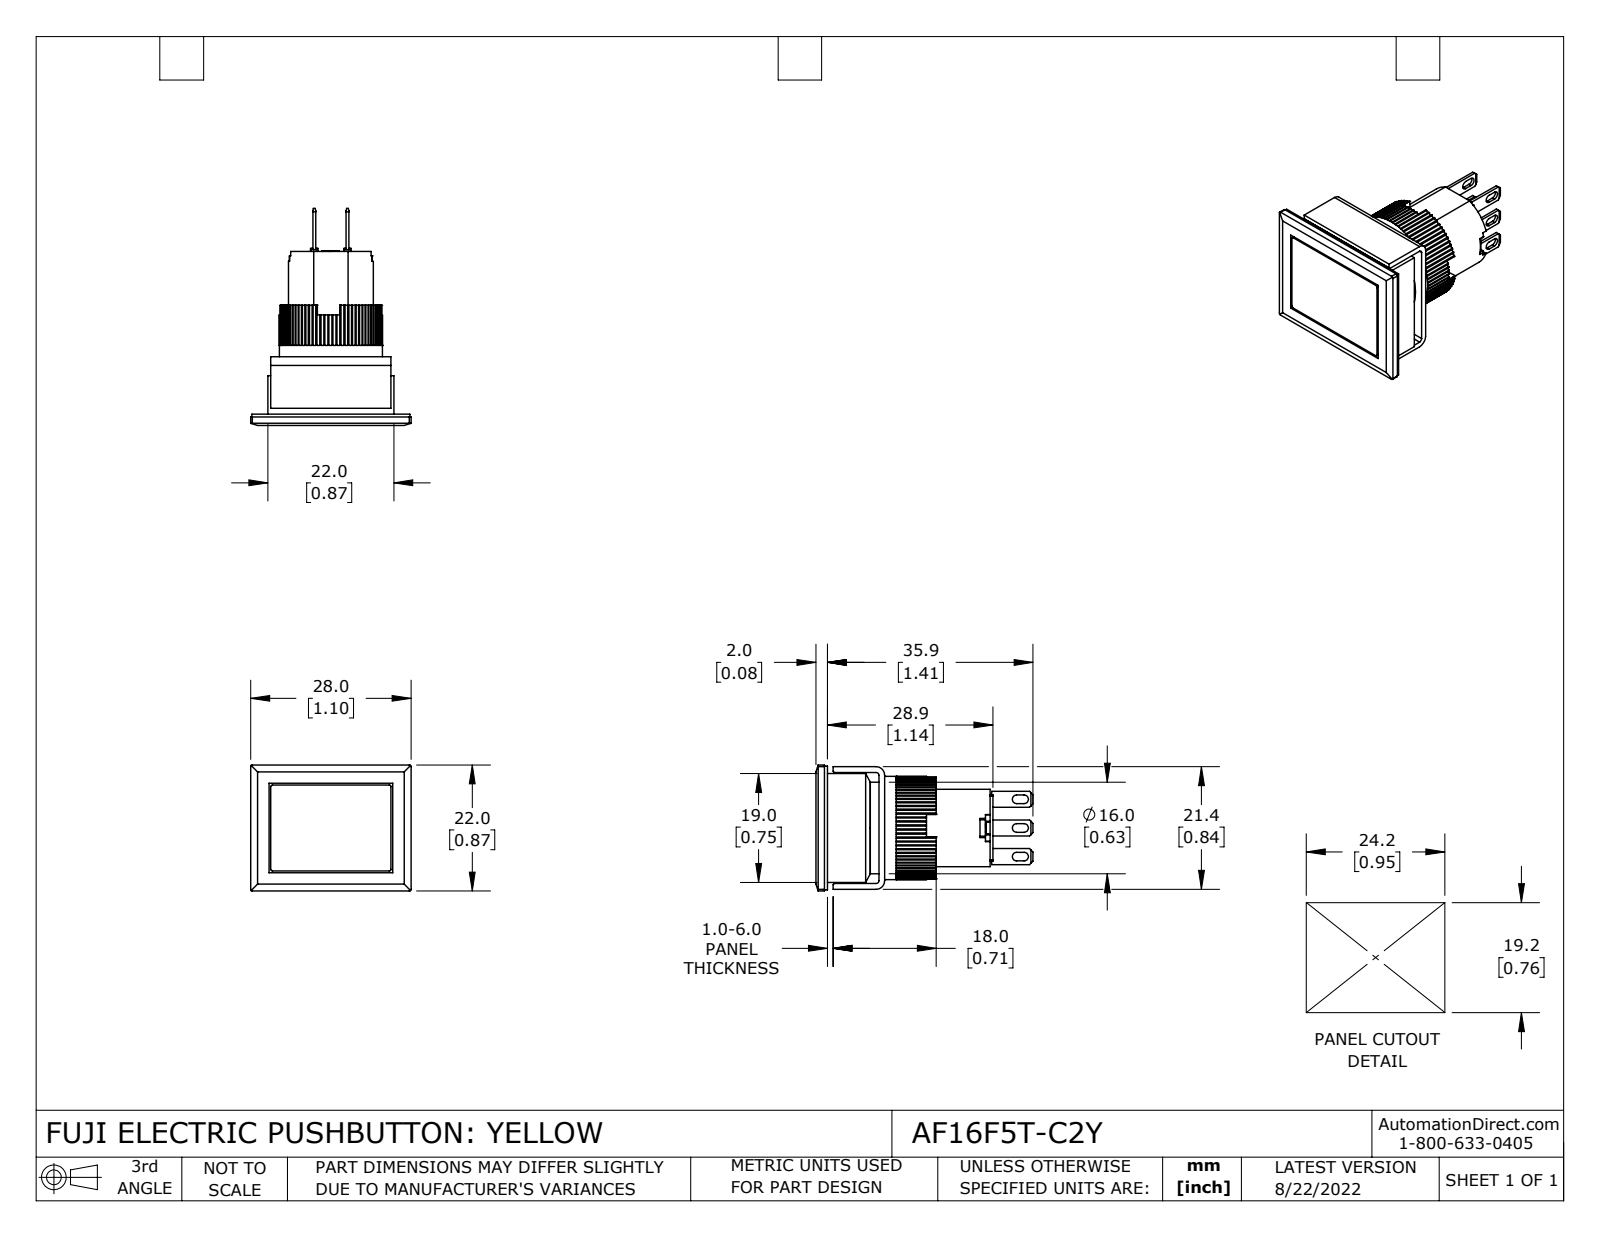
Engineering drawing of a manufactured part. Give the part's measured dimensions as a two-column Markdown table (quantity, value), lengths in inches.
| quantity | value |
| --- | --- |
| part name | AF16F5T-C2Y |
| STEP written by | SolidWorks 2021 (CONFIG_CONTROL_DESIGN) |
| units | inches |
| bodies | 12 solids, 798 faces (620 planar, 176 cylindrical, 2 other) |
| overall size | 1.492 × 1.102 × 0.866 |
| volume | 0.541 in³ |
| surface area | 11.85 in² |
| round holes (diameter × count) | 0.039 × 1, 0.709 × 1 |
| round bosses / shafts (diameter × count) | 0.63 × 1, 0.583 × 1 |
| partial cylindrical surfaces (radius × count) | 0.01 × 80, 0.008 × 12, 0.012 × 8, 0.03 × 6, 0.02 × 2, 0.059 × 2 |
| main face-to-face distances | 0.374, 0.059, 0.02, 0.142, 0.039, 0.315, 0.232, 0.083, 0.079, 0.756 |
